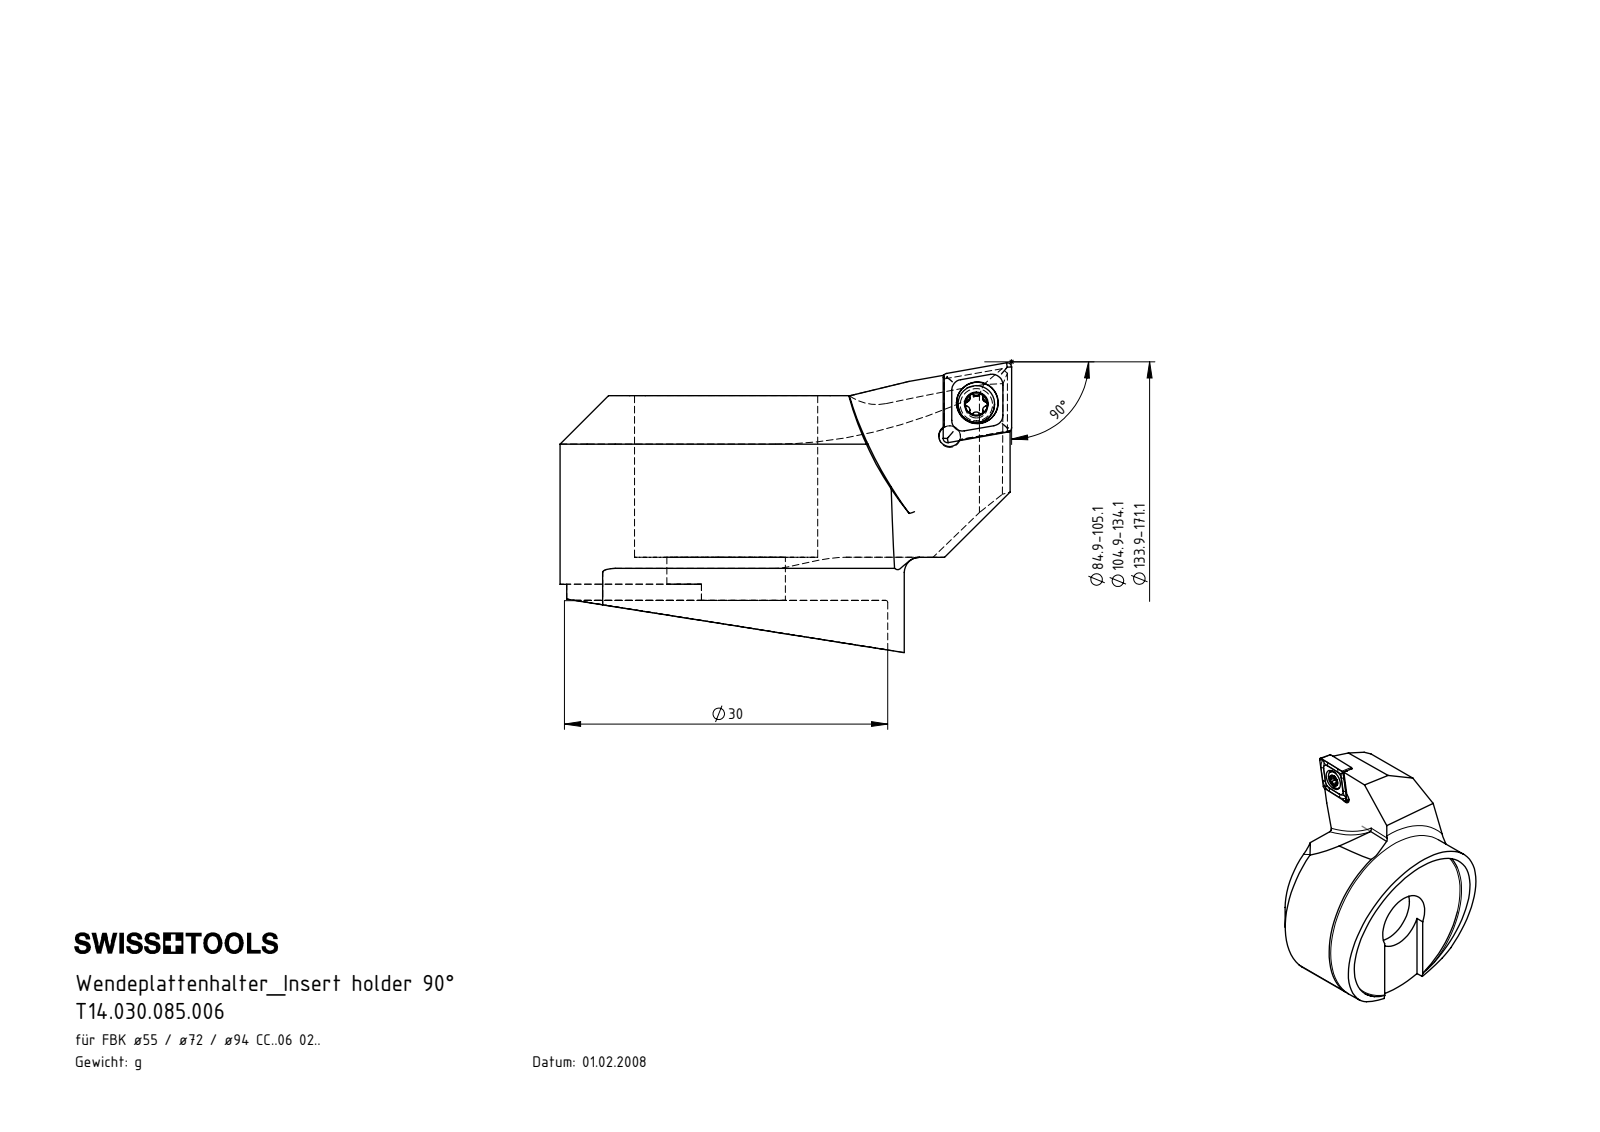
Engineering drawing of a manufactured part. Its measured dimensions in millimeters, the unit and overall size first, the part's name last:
Units: millimetres
Overall size (bounding box): 41.9 × 33.2 × 26.89
Round holes (diameter × count): ⌀2 ×1, ⌀2.05 ×1, ⌀2.8 ×1, ⌀3.85 ×1, ⌀11 ×1, ⌀17 ×1, ⌀30 ×1
Round bosses / shafts (diameter × count): ⌀3.4 ×1, ⌀2.5 ×1
Partial cylindrical surfaces — rounded edges, fillets, slot ends (radius × count): R0.21 ×6, R0.36 ×5, R0.5 ×2, R10 ×2, R0.36 ×1, R5 ×1, R16.55 ×1, R16.6 ×1
Main face-to-face distances: 19, 15, 4, 1.5, 17.5, 2.5, 2.18, 10, 2.38, 0.9
Hole centre spacings: 3.86, 4.01
Volume: 13 387 mm³ · Surface area: 5 350 mm²
Bodies: 3 solids, 116 faces (41 planar, 31 cylindrical, 44 other)
Part name (STEP PRODUCT): CCMT060204; F55-WCA.001.022_D_fertigbearbeitet; F55.WCA.001.022; WCA-ER2.001.006_A
STEP written by: SolidWorks 2017 (AUTOMOTIVE_DESIGN)
